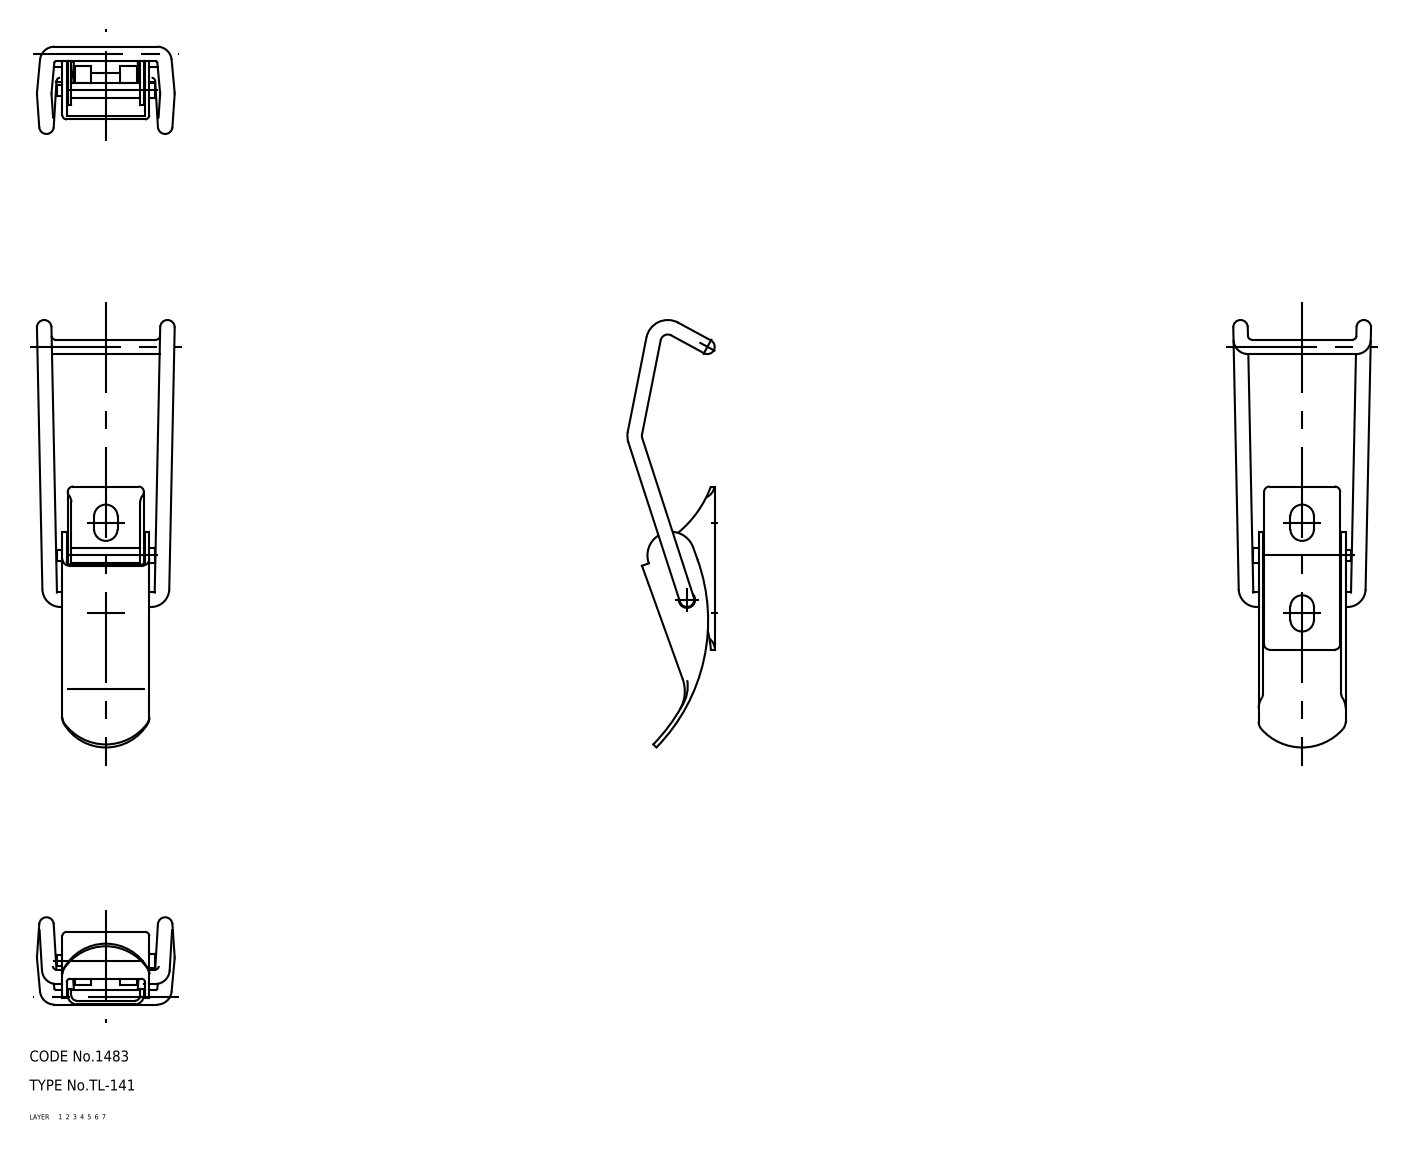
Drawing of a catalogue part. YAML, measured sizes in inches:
part_name: "67116274; 67116287; 67116300; 67116313"
step_written_by: "CADfix (AUTOMOTIVE_DESIGN)"
units: inches
bodies: {solids: 4, faces: 116, planar: 0, cylindrical: 0, other: 116}
overall_size: [4.646, 1.496, 0.948]
volume: 0.434
surface_area: 16.57
